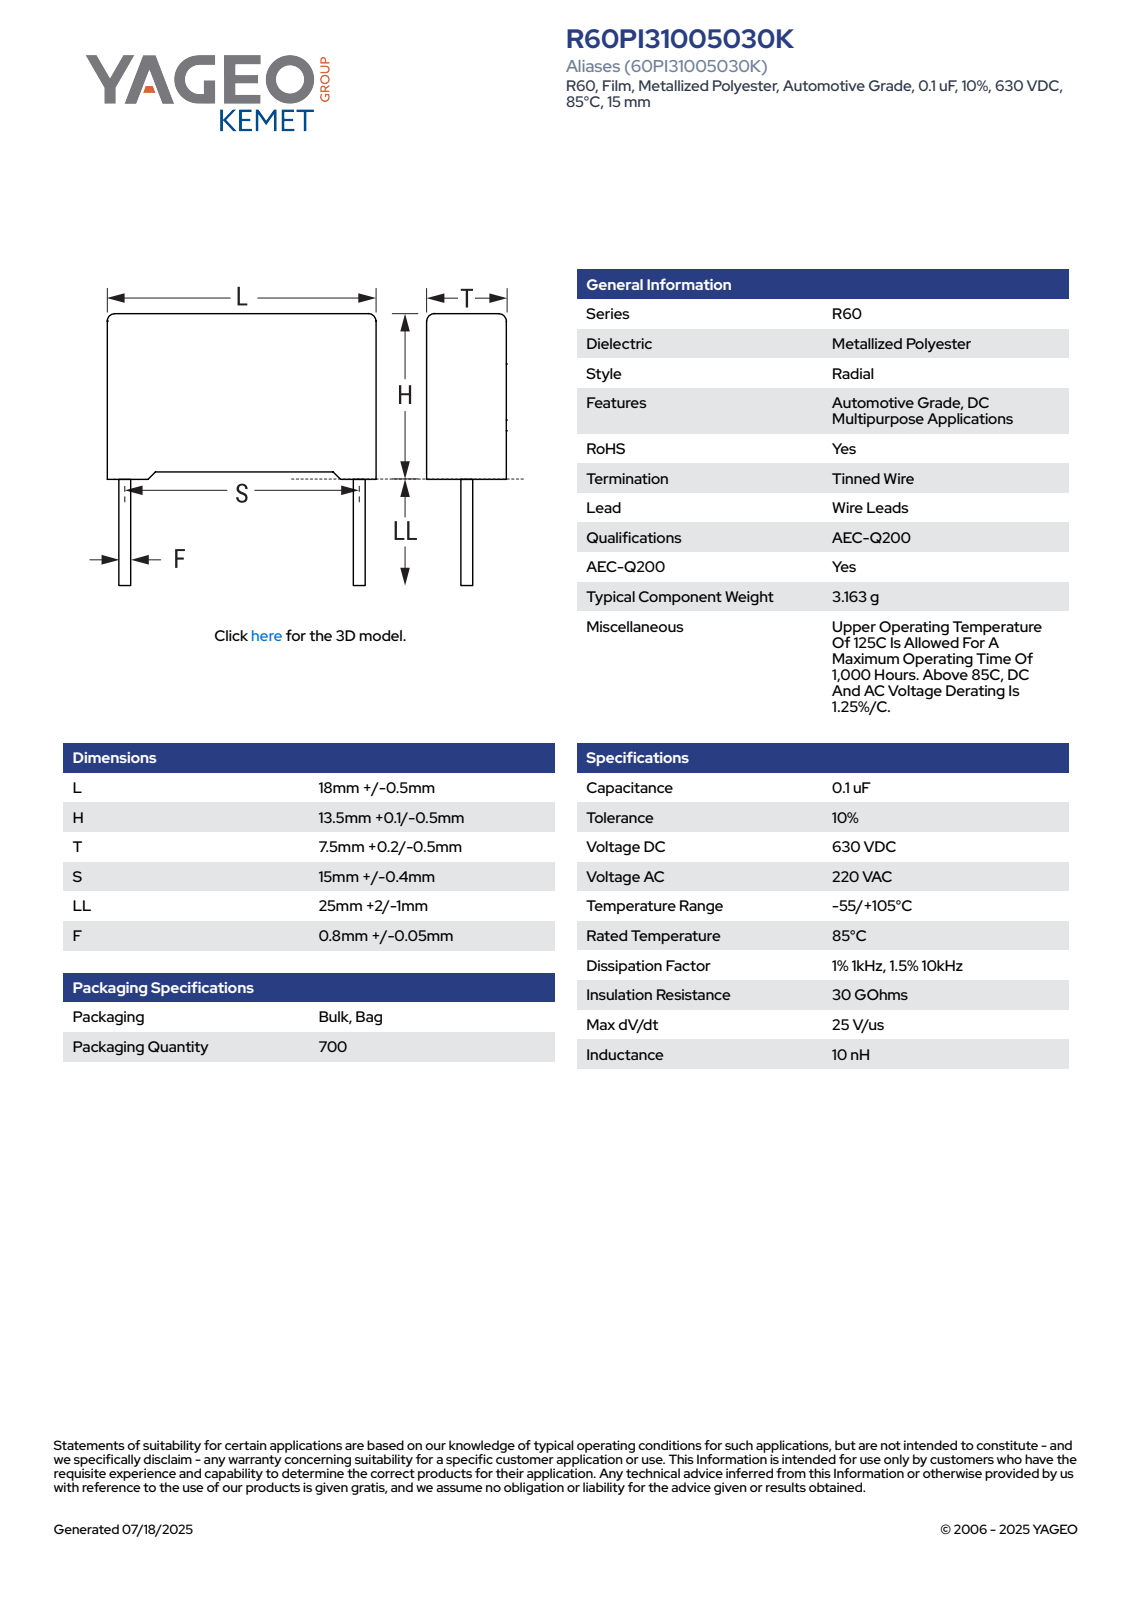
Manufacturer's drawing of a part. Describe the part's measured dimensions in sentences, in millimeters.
The part is named "CFR_RB2_18X13.5X7.5_L18.5H13.6T7.7S15LL27F0.85". Its 3-D file was written by "SolidWorks 2021 (AUTOMOTIVE_DESIGN)". It is 4 solids with 85 faces: 77 planar, 8 cylindrical and 0 other. Overall it measures 40.6 by 18.5 by 7.71 millimeters. Its volume is 1 876 cubic millimeters and its surface area 1 175 square millimeters. Round bosses or shafts: 2 of diameter 0.85. Partial cylindrical surfaces (rounded edges, fillets, slot ends): 4 of radius 0.5. The main face-to-face distances are 7.7, 12.85, 18.5, 0.62, 0.75, 13.6, 7.08, 0.47, 13.13, 17.88.
